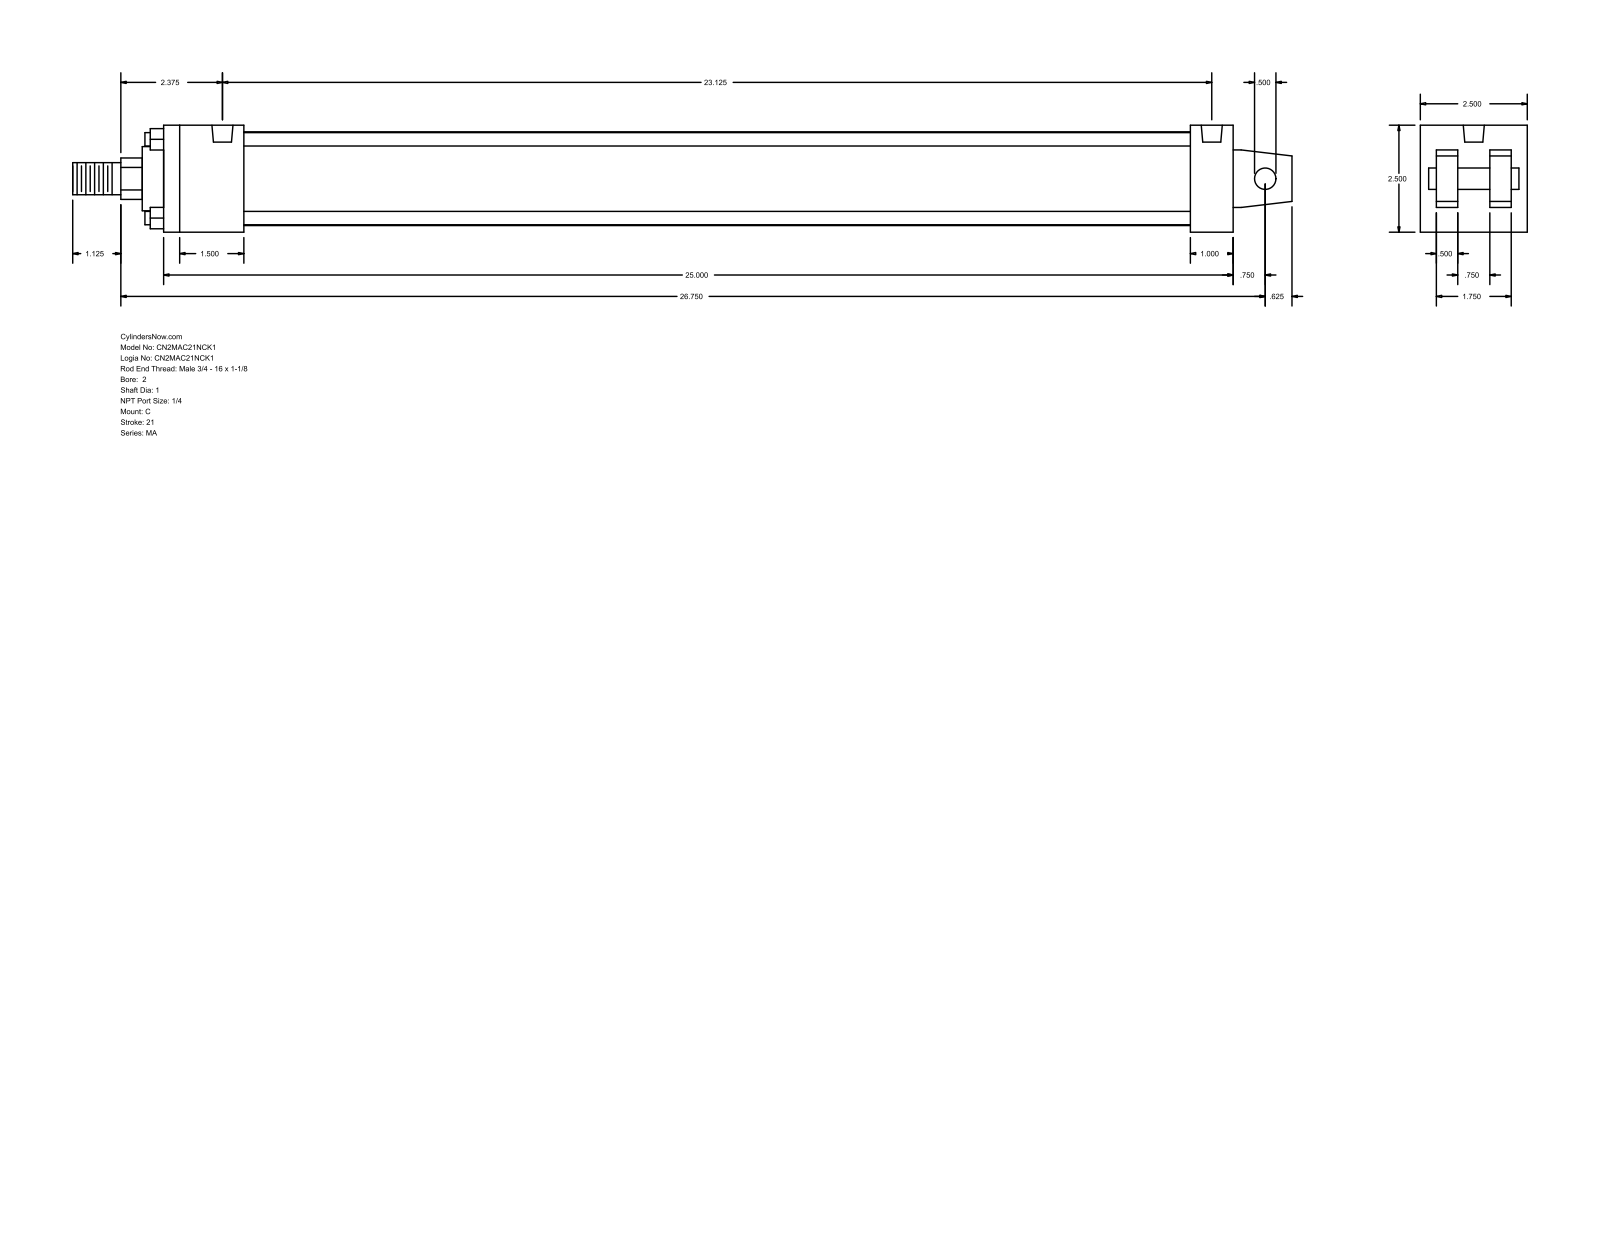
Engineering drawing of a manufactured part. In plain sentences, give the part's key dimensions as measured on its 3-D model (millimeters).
The part is named "MA_C__0200_1". Its 3-D file was written by "GSSL Pune (CONFIG_CONTROL_DESIGN)". It is 0 solids with 103 faces: 76 planar, 27 cylindrical and 0 other. Overall it measures 723.9 by 63.5 by 63.5 millimeters. Round holes: 4 of diameter 7.94, 2 of diameter 12.49. Round bosses or shafts: 4 of diameter 7.94, 1 of diameter 55.63, 1 of diameter 38.1, 1 of diameter 25.4, 1 of diameter 19.05, 1 of diameter 12.7. Partial cylindrical surfaces (rounded edges, fillets, slot ends): 1 of radius 12.29. The main face-to-face distances are 63.5, 12.7, 635, 22.22, 41.28, 9.52, 53.98, 31.76, 47.63, 25.4. The hole center spacings are 587.37.
